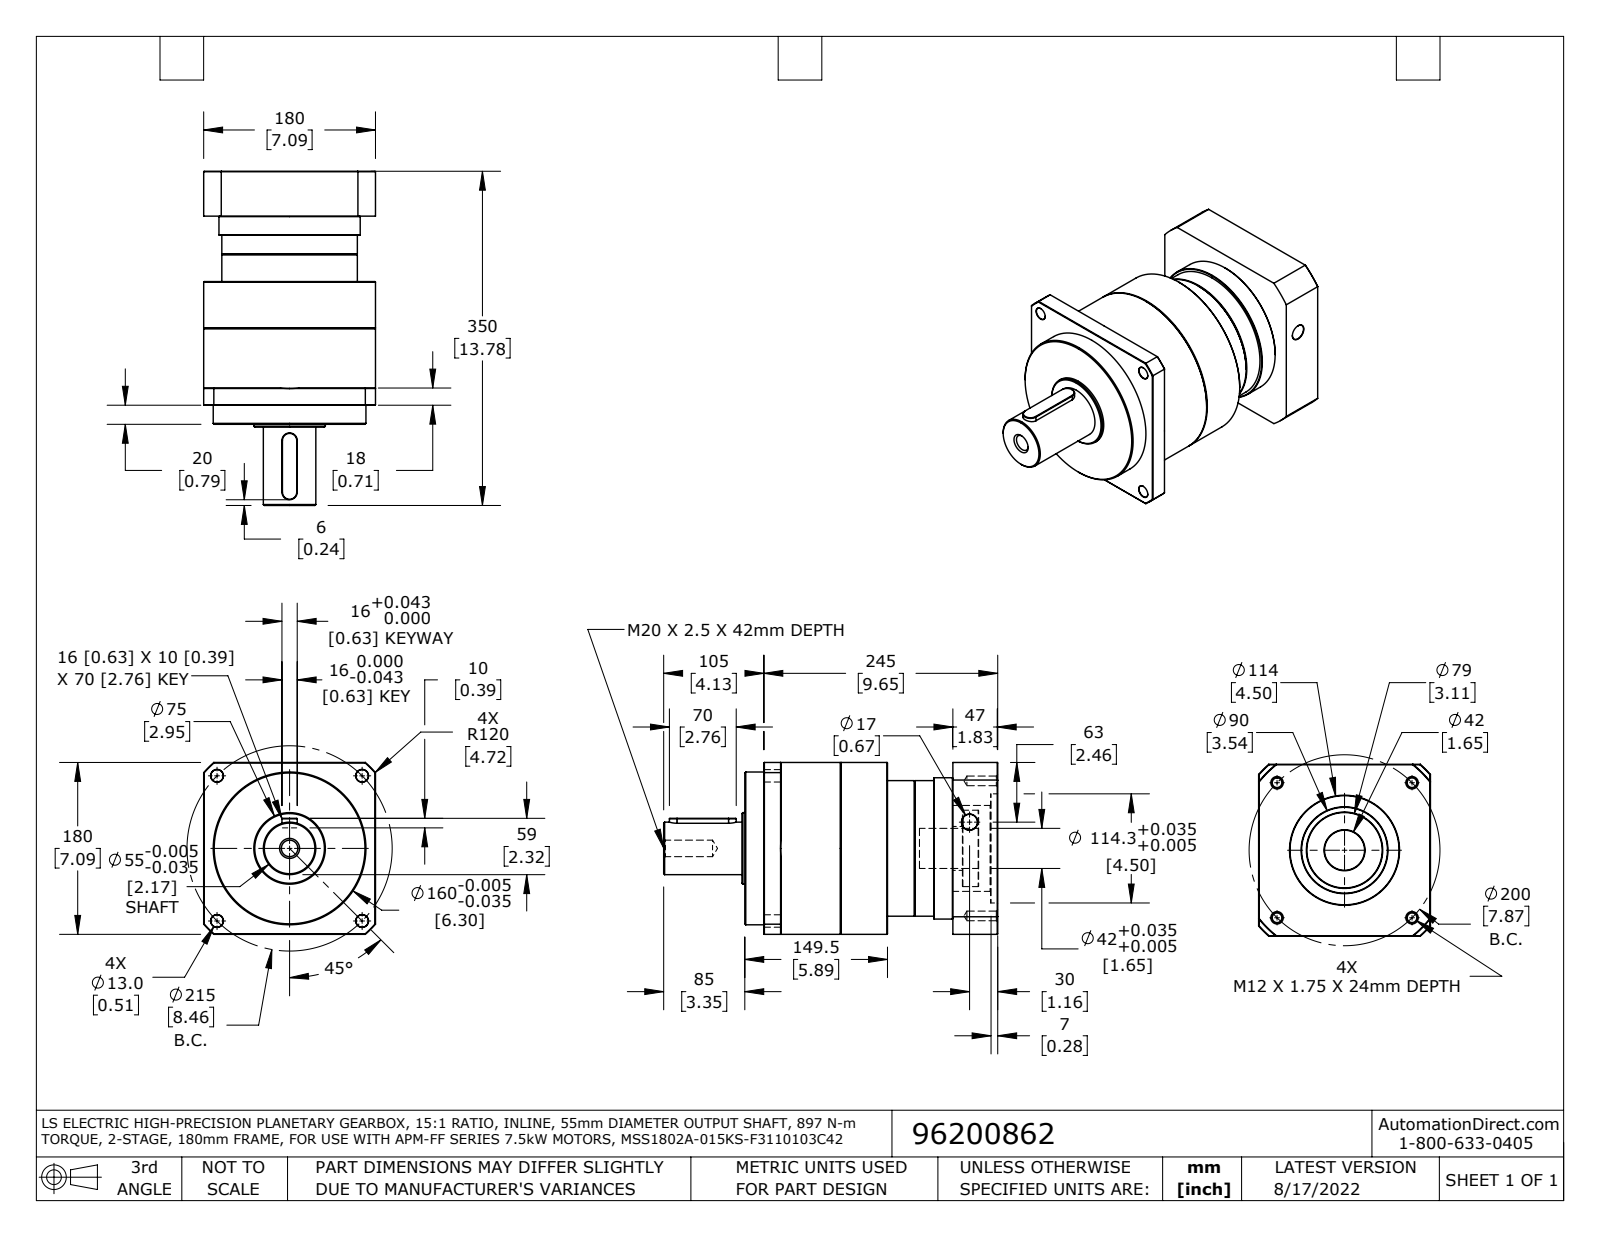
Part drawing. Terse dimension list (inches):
name: MSS1802A-F3110103 nc fxt
written by: SolidWorks 2021 (AUTOMOTIVE_DESIGN)
unit: in
bodies: 3 solids, 187 faces (48 planar, 56 cylindrical, 83 other)
size: 13.78 × 7.087 × 7.087
volume: 383.2 in³; area: 553.5 in²
holes: 4× ⌀0.398, 4× ⌀0.512, 1× ⌀0.65, 1× ⌀0.681, 1× ⌀1.654, 1× ⌀3.543, 1× ⌀4.5
bosses: 1× ⌀7.087, 1× ⌀6.299, 1× ⌀5.827, 1× ⌀5.591, 1× ⌀3.15, 1× ⌀2.953, 1× ⌀2.165, 1× ⌀1.811
rounds: 2× R0.315, 1× R4.528, 1× R4.724
face distances: 1.575, 7.087, 1.85, 3.425, 0.787, 7.008, 10.433, 8.583, 9.646, 7.795
hole spacings: 5.78, 0.295, 3.937, 5.568, 4.232, 4.232, 5.781, 5.985
